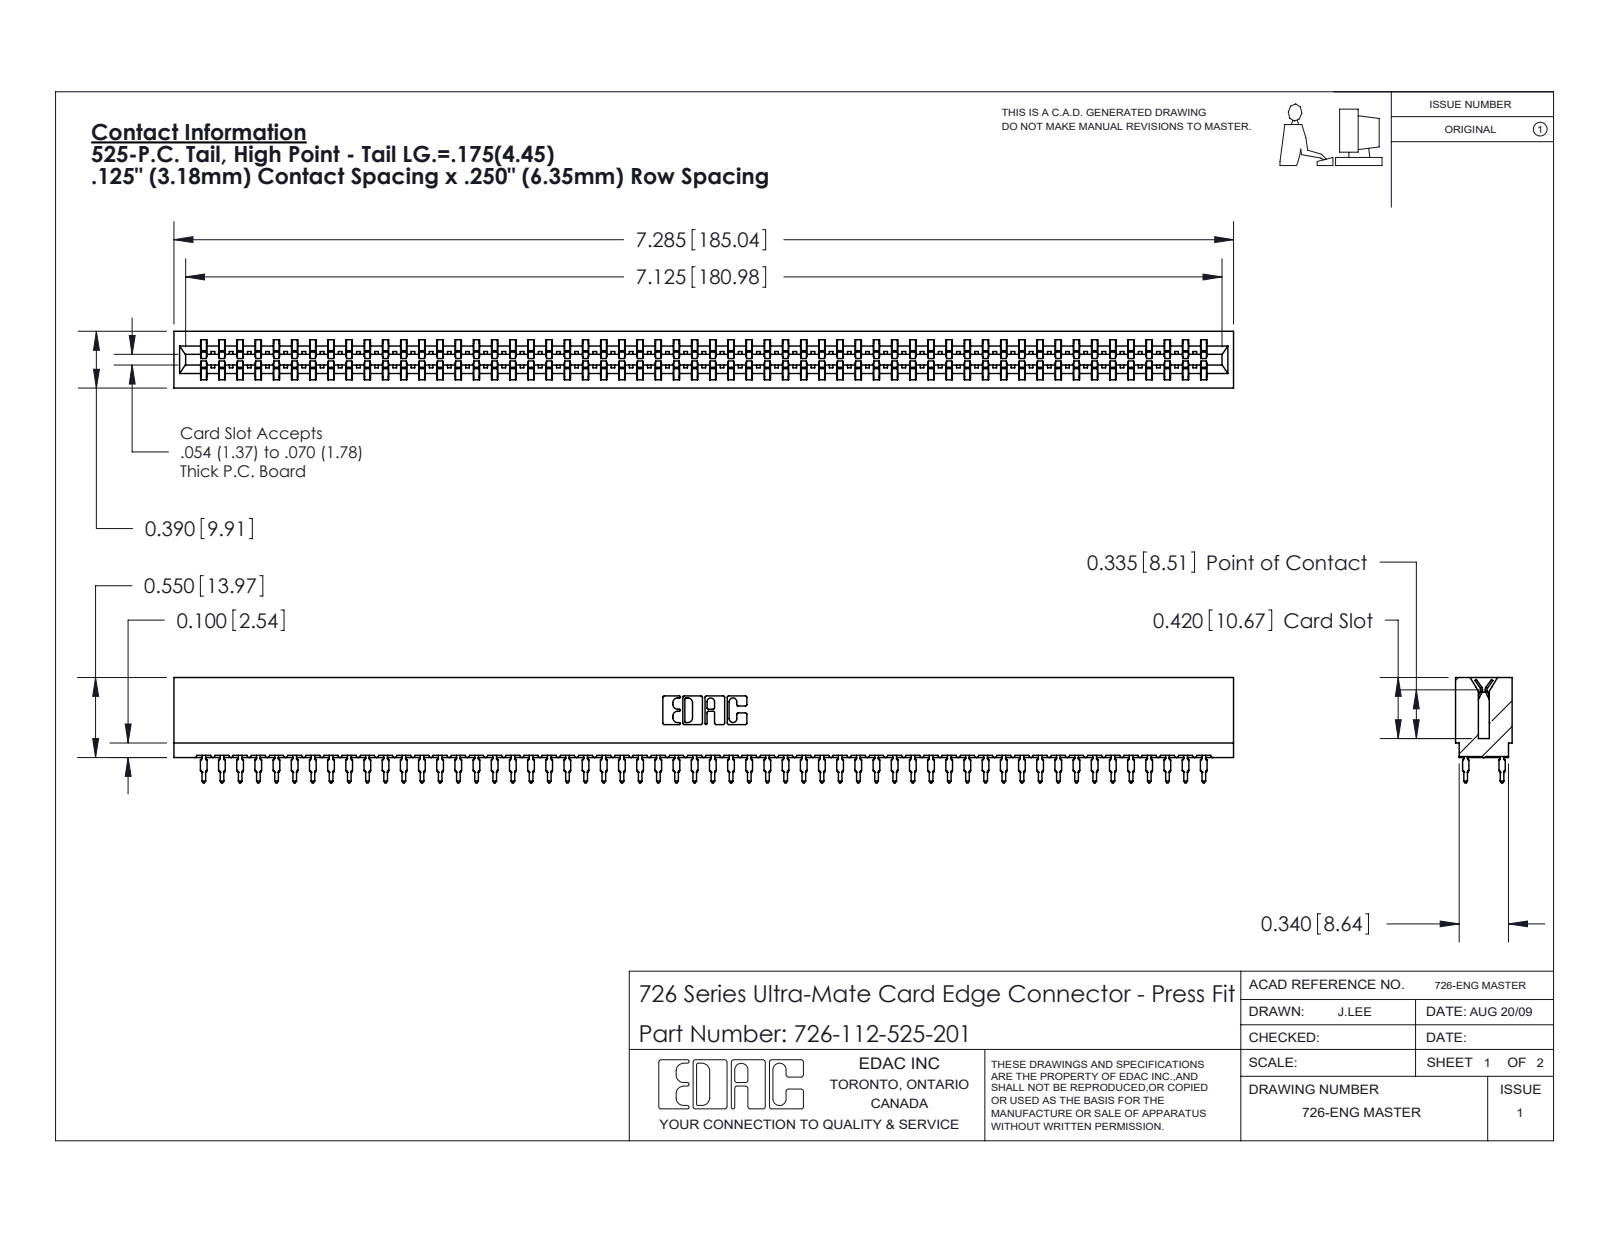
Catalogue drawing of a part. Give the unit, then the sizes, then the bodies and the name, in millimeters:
Units: millimetres
Overall size (bounding box): 185 × 18.4 × 9.9
Partial cylindrical surfaces — rounded edges, fillets, slot ends (radius × count): R0.5 ×224, R0.4 ×57, R0.3 ×22, R0.1 ×8, R0.3 ×8, R0.2 ×6, R0.8 ×6, R0.7 ×3
Main face-to-face distances: 1.4, 8.5, 9.9, 0.6, 7.8, 6.4, 7, 2.1, 9.3, 0.8
Volume: 16 900 mm³ · Surface area: 28 150 mm²
Bodies: 113 solids, 10121 faces (5207 planar, 2002 cylindrical, 2912 other)
Part name (STEP PRODUCT): 746-292-001_525; 726 Part_.515 Slot Depth - 01; 726-112-525-201
STEP written by: SolidWorks 2020 (CONFIG_CONTROL_DESIGN)
